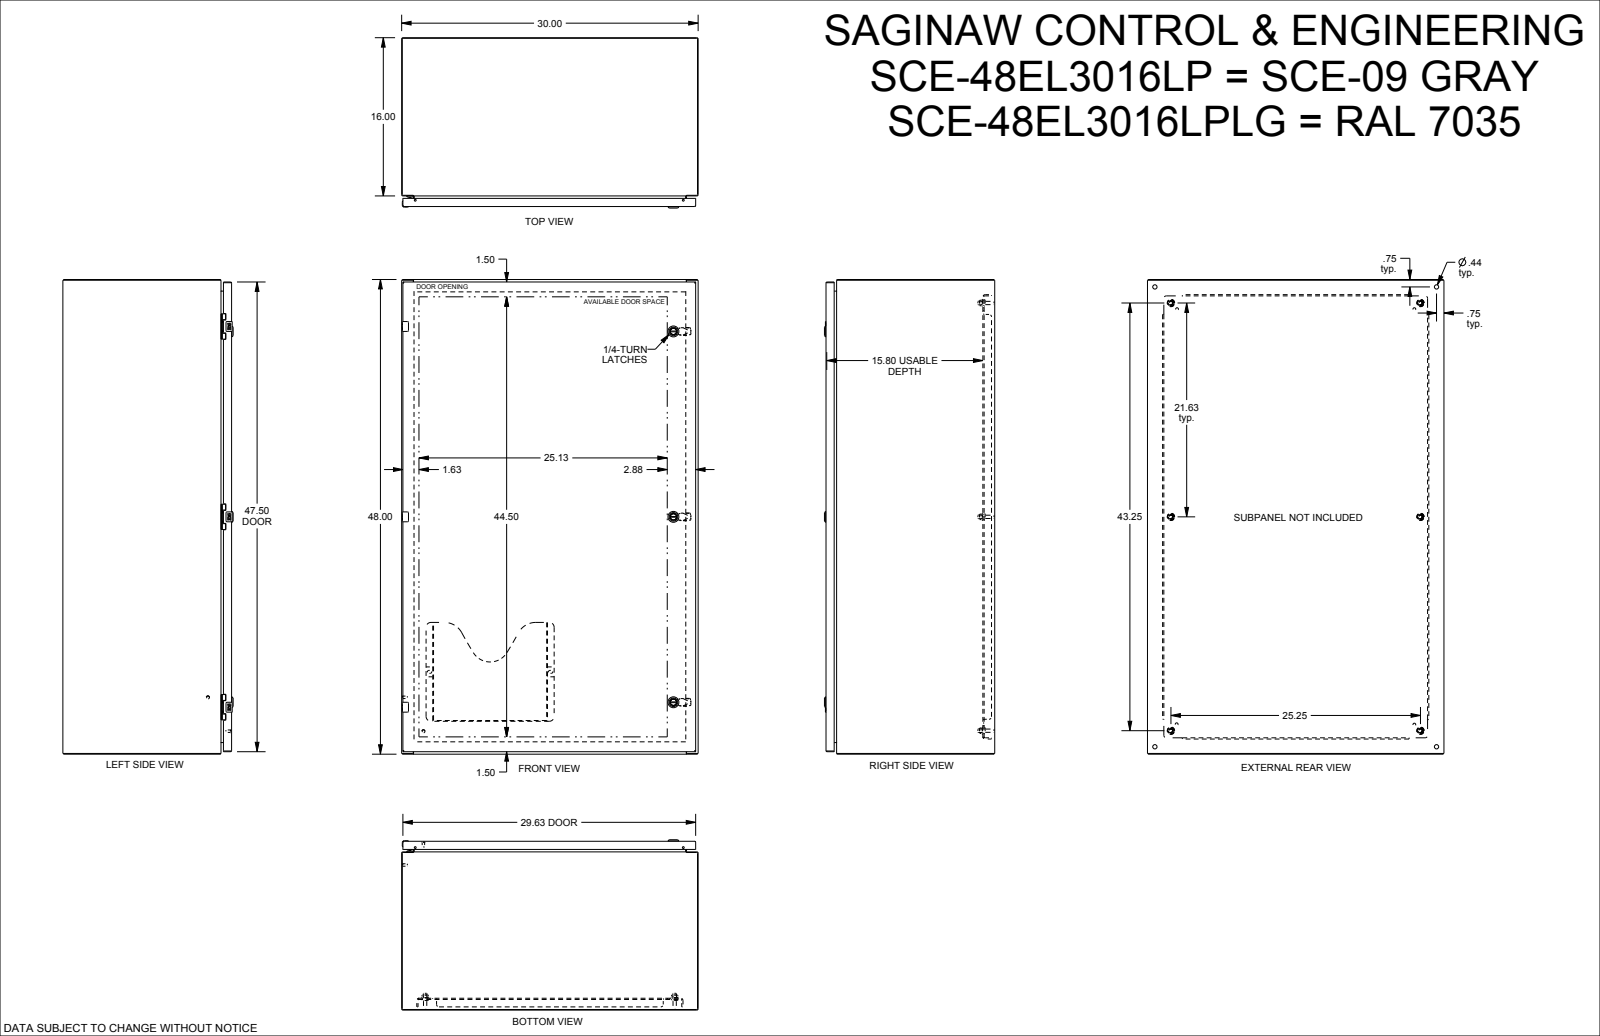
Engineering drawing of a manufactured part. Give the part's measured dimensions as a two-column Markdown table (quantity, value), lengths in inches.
| quantity | value |
| --- | --- |
| part name | SCE-48EL3016LP |
| STEP written by | SolidWorks 2019 (CONFIG_CONTROL_DESIGN) |
| units | inches |
| bodies | 0 solids, 3818 faces (1807 planar, 1058 cylindrical, 953 other) |
| overall size | 48 × 30 × 17.23 |
| round holes (diameter × count) | 0.172 × 6, 0.205 × 6, 0.244 × 6, 0.266 × 6, 0.367 × 6, 0.375 × 6, 0.5 × 6, 0.281 × 4, 0.437 × 4, 0.04 × 3, 0.156 × 3, 0.197 × 3 |
| round bosses / shafts (diameter × count) | 0.17 × 9, 0.366 × 6, 0.332 × 6, 0.25 × 6, 0.24 × 6, 0.248 × 4, 0.196 × 4, 1.102 × 3 |
| partial cylindrical surfaces (radius × count) | 0.012 × 82, 0.01 × 40, 0.015 × 32, 0.02 × 28, 0.04 × 17, 0.025 × 16, 0.1 × 16, 0.03 × 15 |
| main face-to-face distances | 0.075, 0.075, 29.925, 16.998, 16.923, 17.073, 16.998, 1.2, 15.873, 0.125 |
| hole center spacings | 19.25, 0.985, 38.5, 0.02, 0.493, 0.494, 4.493, 18.265 |
